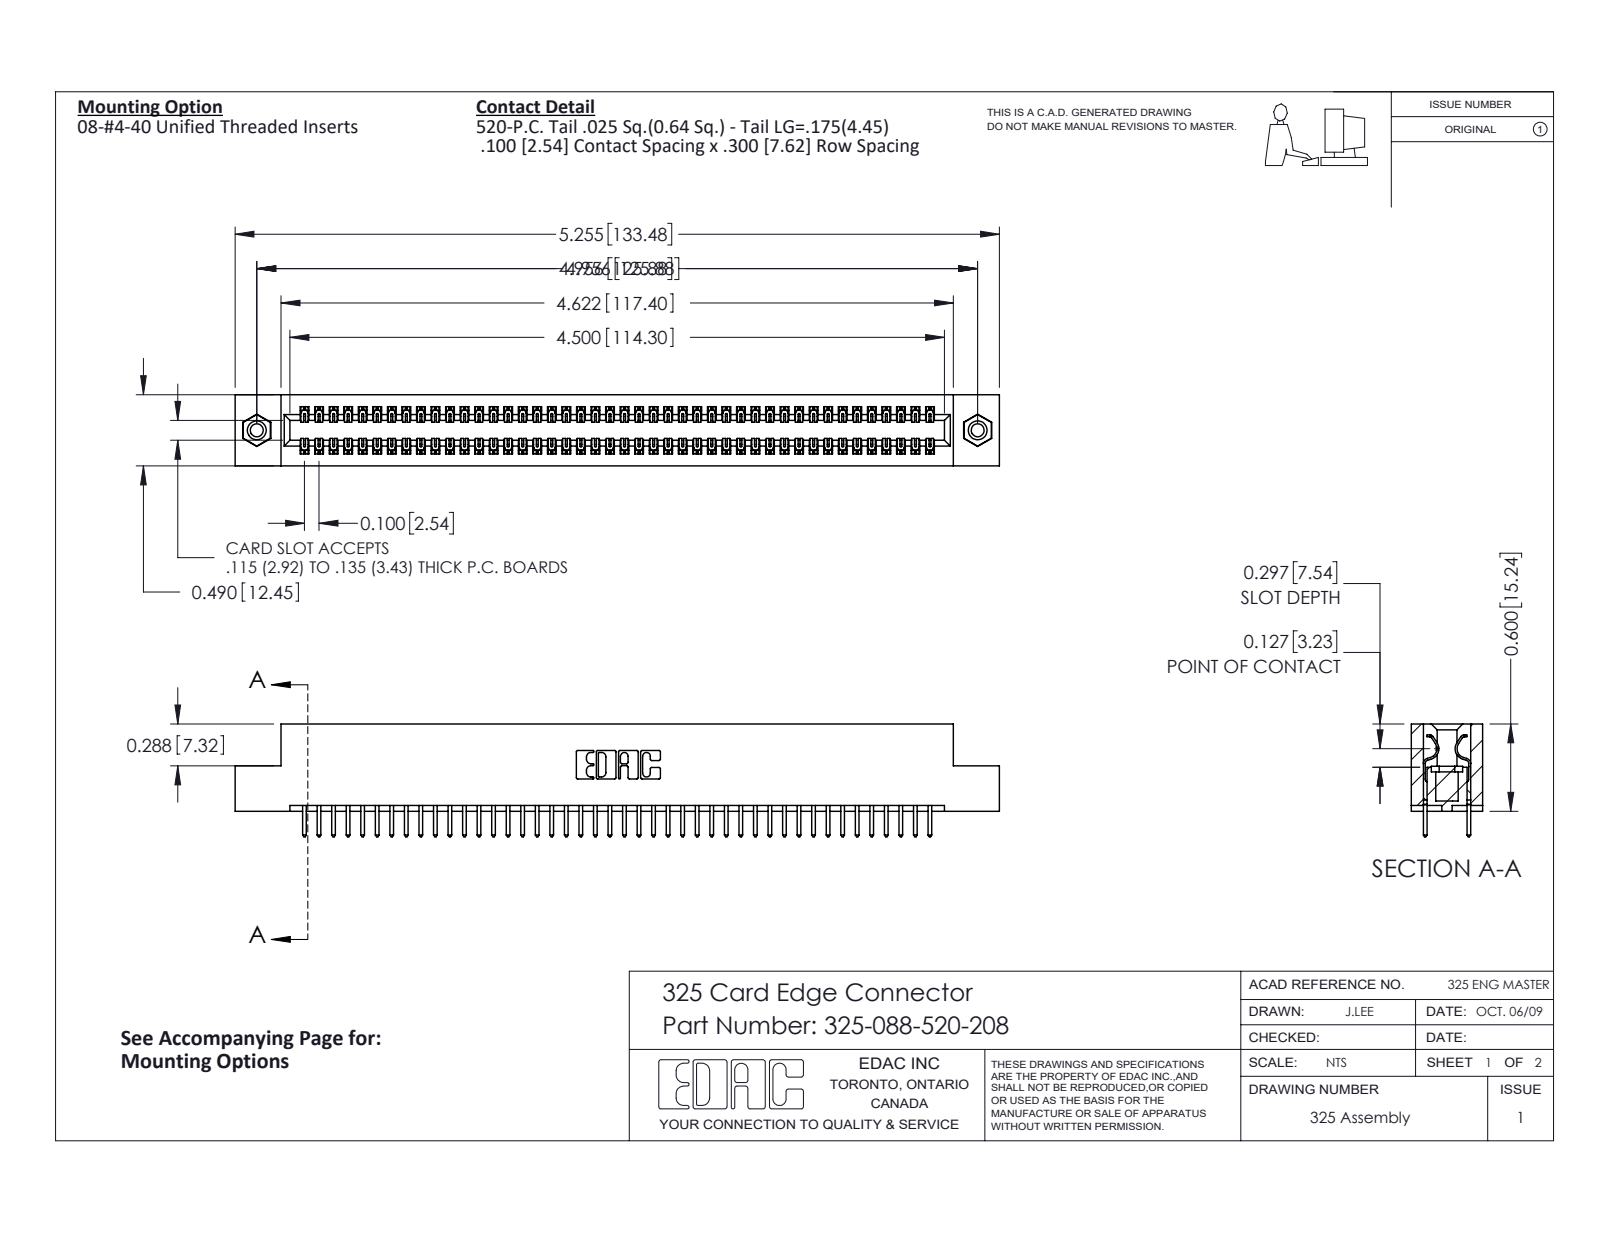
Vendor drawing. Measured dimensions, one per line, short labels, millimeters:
name: 325-292-001_325-293-120; 325 Part_TI; 345-250-001_345-250-003-102; 325-088-520-208
written by: SolidWorks 2016 (CONFIG_CONTROL_DESIGN)
unit: mm
bodies: 91 solids, 4750 faces (3270 planar, 1464 cylindrical, 16 other)
size: 133.5 × 19.7 × 12.4
volume: 17 220 mm³; area: 20 740 mm²
holes: 2× ⌀2.3, 2× ⌀3.2, 2× ⌀4.1
bosses: 2× ⌀3.9
rounds: 132× R0.2, 88× R0.3, 22× R0.3, 6× R0.2, 6× R0.8, 3× R0.7, 2× R0.4, 2× R0.6
face distances: 2.1, 10.3, 7.6, 12.4, 2.7, 9.7, 0.6, 8.3, 7, 14.2
hole spacings: 125.9
